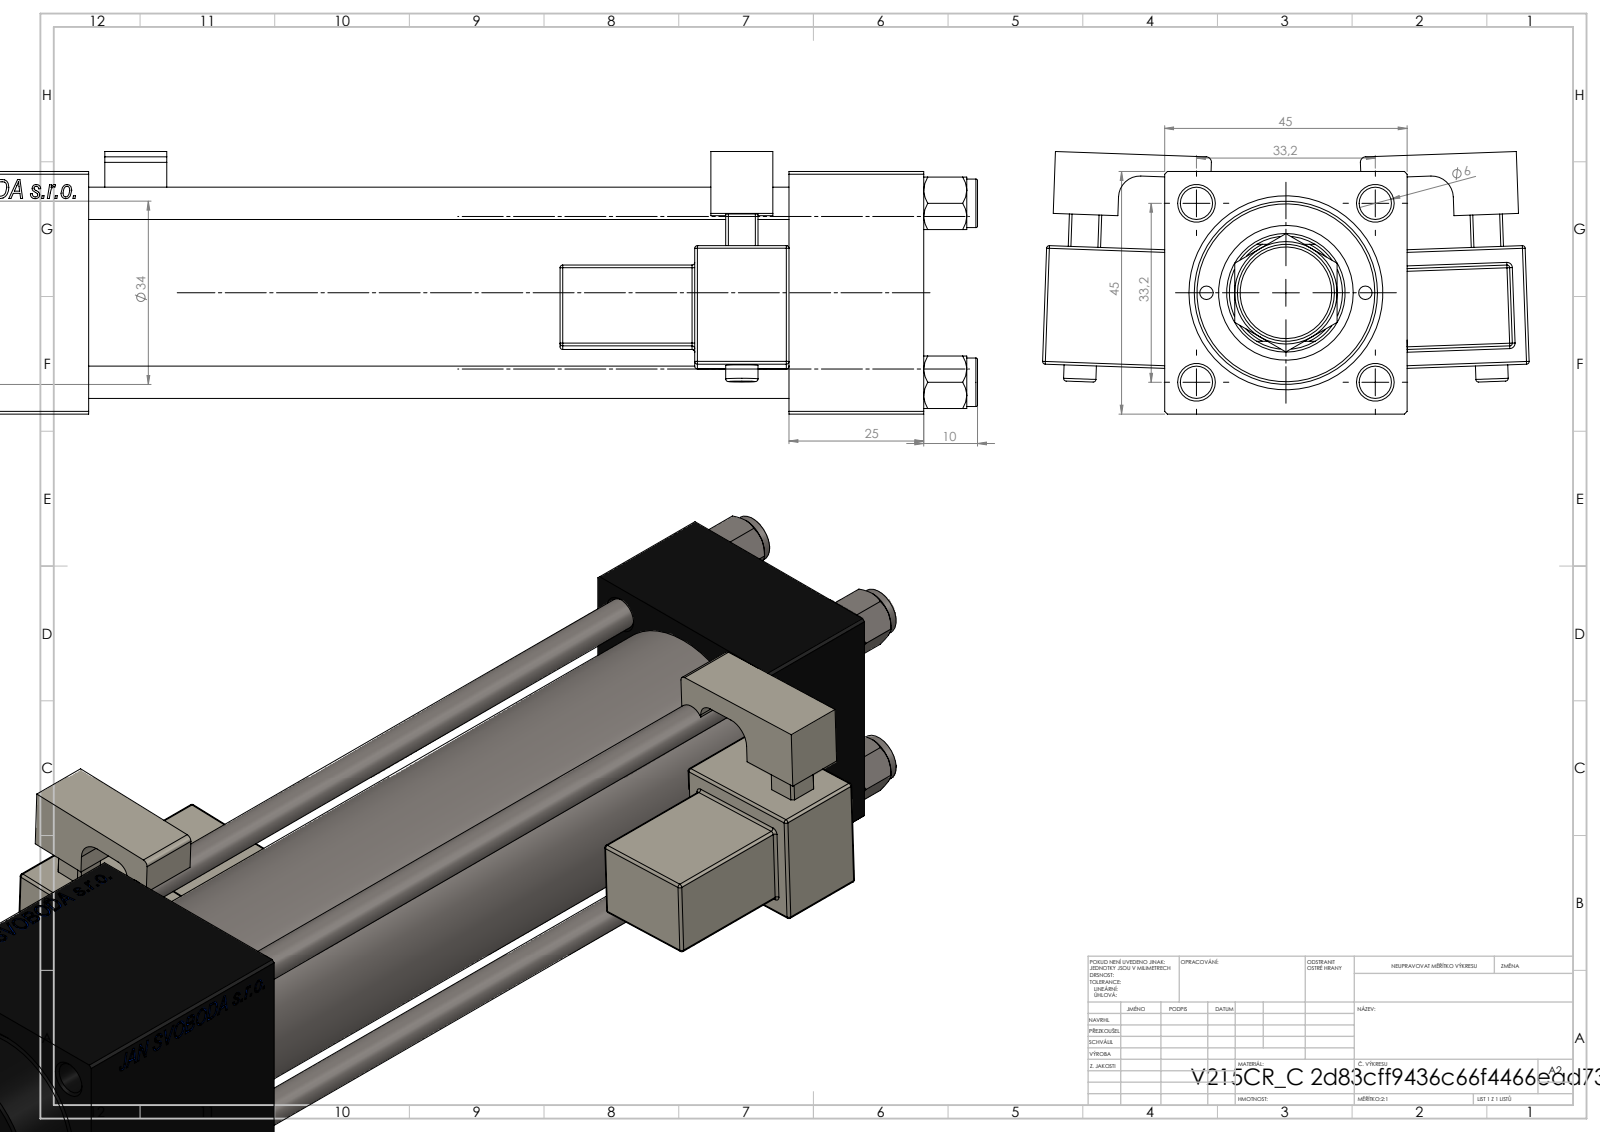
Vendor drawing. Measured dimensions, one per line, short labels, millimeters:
name: NUT_M5_C; V215_VC_A; V215CR_VCP_C; V215CR_C_TYCINKA (+3 more)
written by: SolidWorks 2019 (CONFIG_CONTROL_DESIGN)
unit: mm
bodies: 14 solids, 1363 faces (605 planar, 154 cylindrical, 604 other)
size: 271 × 90.31 × 48.72
volume: 324 266 mm³; area: 115 421 mm²
holes: 4× ⌀6, 2× ⌀2.5, 2× ⌀7, 2× ⌀13.16, 2× ⌀20, 1× ⌀10.5, 1× ⌀22, 1× ⌀24, 1× ⌀25, 1× ⌀32, 1× ⌀33
bosses: 4× ⌀9, 2× ⌀6, 1× ⌀38, 1× ⌀34, 1× ⌀18, 1× ⌀11
rounds: 48× R0.5, 2× R1, 2× R2.5, 2× R4, 1× R10.5
face distances: 45, 25, 3, 155, 130, 203, 22.99, 112.5, 178, 13
hole spacings: 16.7, 23.48, 33.2, 35.47, 14.75, 46.95, 29.5, 155.5
